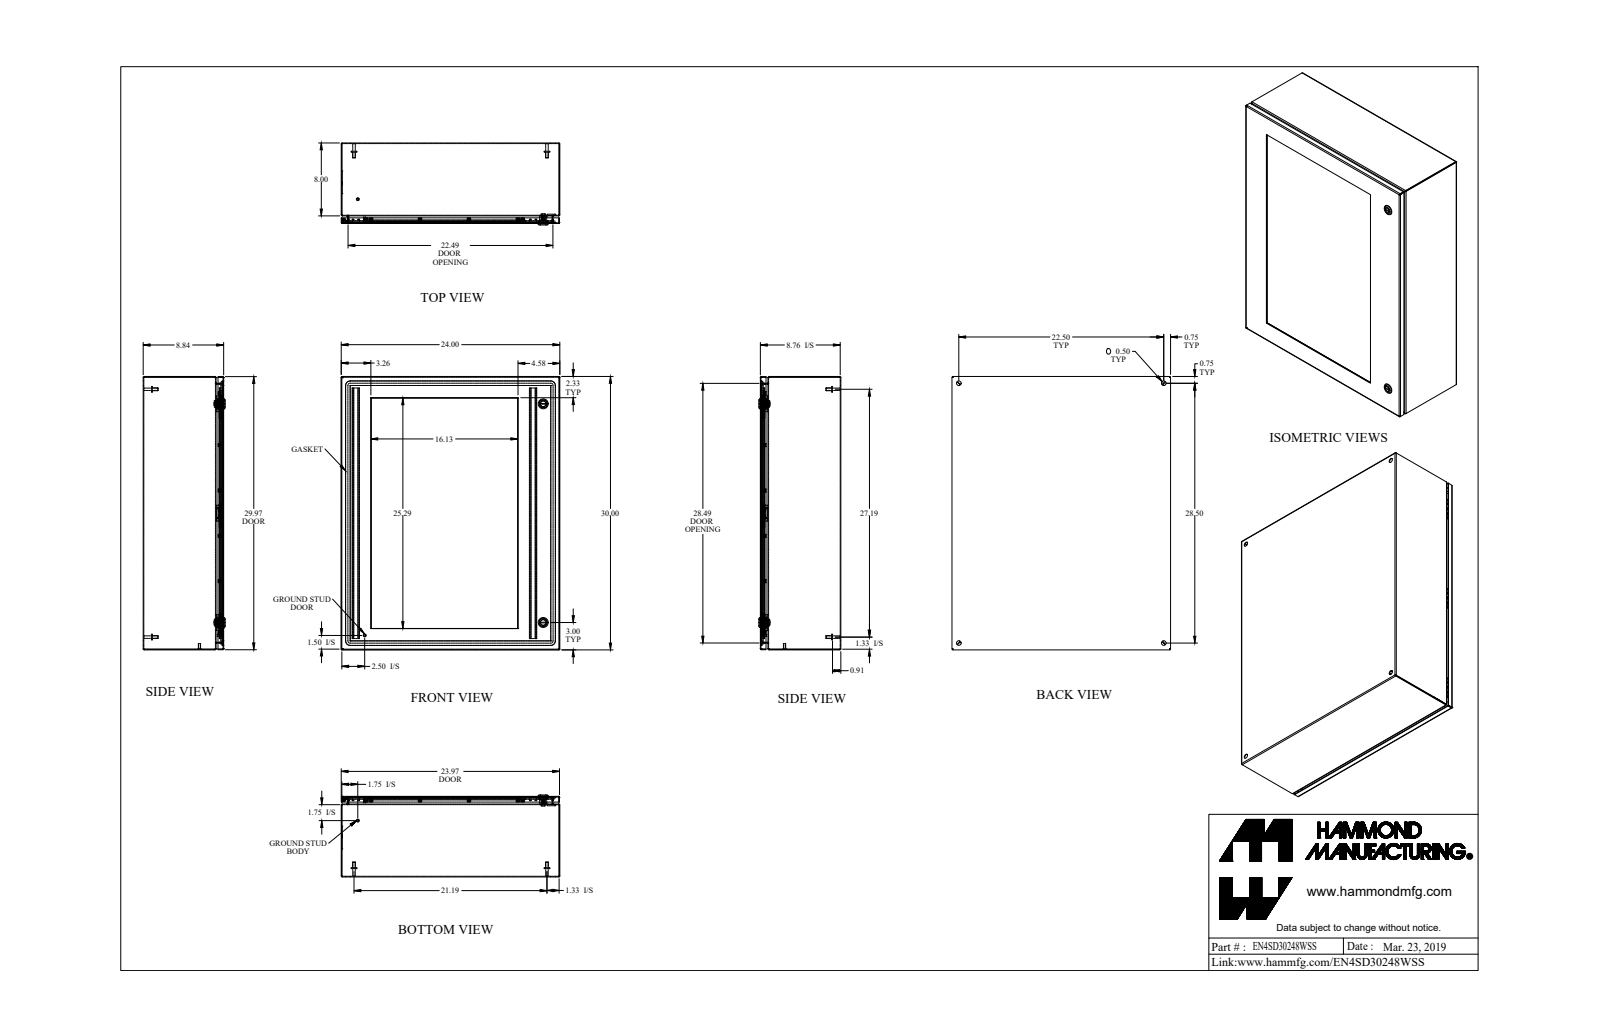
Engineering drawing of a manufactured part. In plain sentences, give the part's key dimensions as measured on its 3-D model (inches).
The part is named "EN4SD30248WSS_Default". Its 3-D file was written by "SolidWorks 2019 (CONFIG_CONTROL_DESIGN)". It is 82 solids with 1690 faces: 861 planar, 517 cylindrical and 312 other. Overall it measures 30 by 24 by 8.997 inches. Its volume is 281.4 cubic inches and its surface area 5 834 square inches. Round holes: 20 of diameter 0.13, 20 of diameter 0.25, 6 of diameter 0.5, 2 of diameter 0.197, 2 of diameter 0.387, 2 of diameter 0.63, 2 of diameter 0.768, 1 of diameter 0.172, 1 of diameter 0.24, 1 of diameter 0.242. Round bosses or shafts: 21 of diameter 0.226, 20 of diameter 0.368, 20 of diameter 0.164, 6 of diameter 0.625, 6 of diameter 0.313, 4 of diameter 0.275, 2 of diameter 1.1, 2 of diameter 0.785. Partial cylindrical surfaces (rounded edges, fillets, slot ends): 20 of radius 0.036, 20 of radius 0.108, 16 of radius 0.25, 12 of radius 0.01, 12 of radius 0.048, 12 of radius 0.125, 6 of radius 0.006, 6 of radius 0.062. The main face-to-face distances are 0.072, 8.765, 8.693, 8.443, 0.25, 8.515, 23.928, 29.928, 0.322, 8.837. The hole center spacings are 9.95, 19.822, 4.975, 17.144, 17.851, 5.372, 5.372, 14.925.
